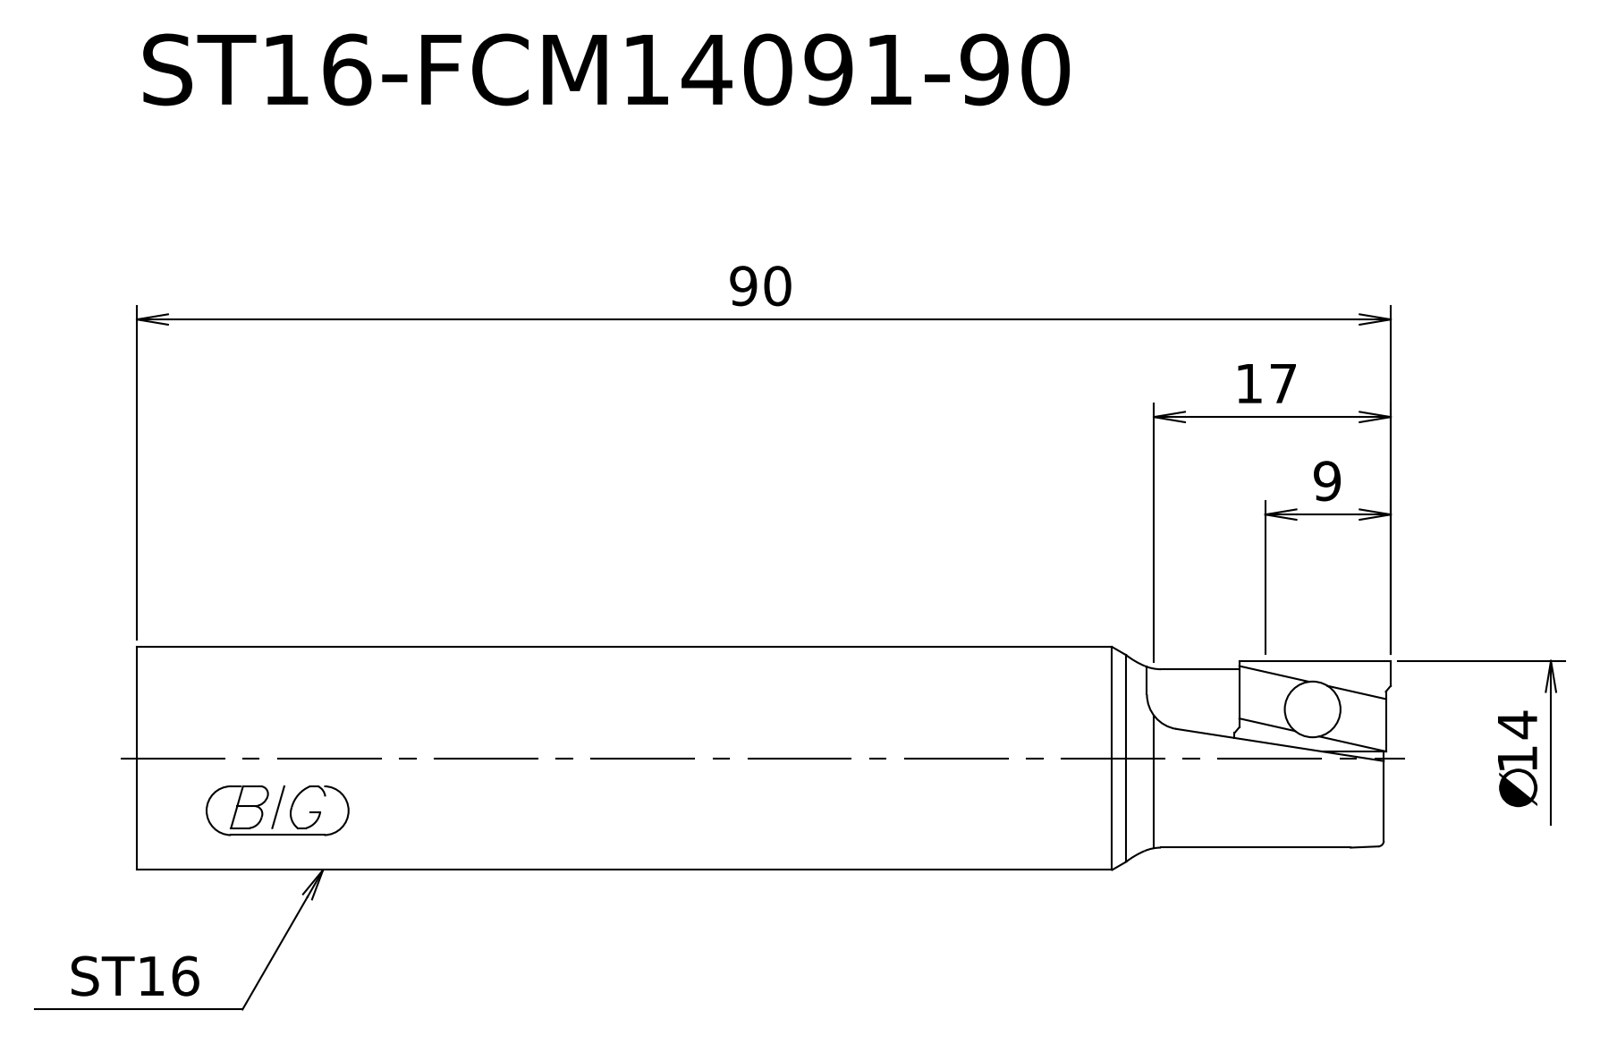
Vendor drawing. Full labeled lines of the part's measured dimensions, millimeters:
STEP written by: Kubotek KeyCreator V8.5.1 (14335) (CONFIG_CONTROL_DESIGN)
Units: millimetres
Bodies: 1 solid, 7 faces (3 planar, 3 cylindrical, 1 other)
Overall size (bounding box): 90 × 16 × 16
Volume: 17 044 mm³ · Surface area: 4 777 mm²
Round bosses / shafts (diameter × count): ⌀16 ×1, ⌀14 ×1, ⌀12.8 ×1
Main face-to-face distances: 90, 10.86, 79.14
